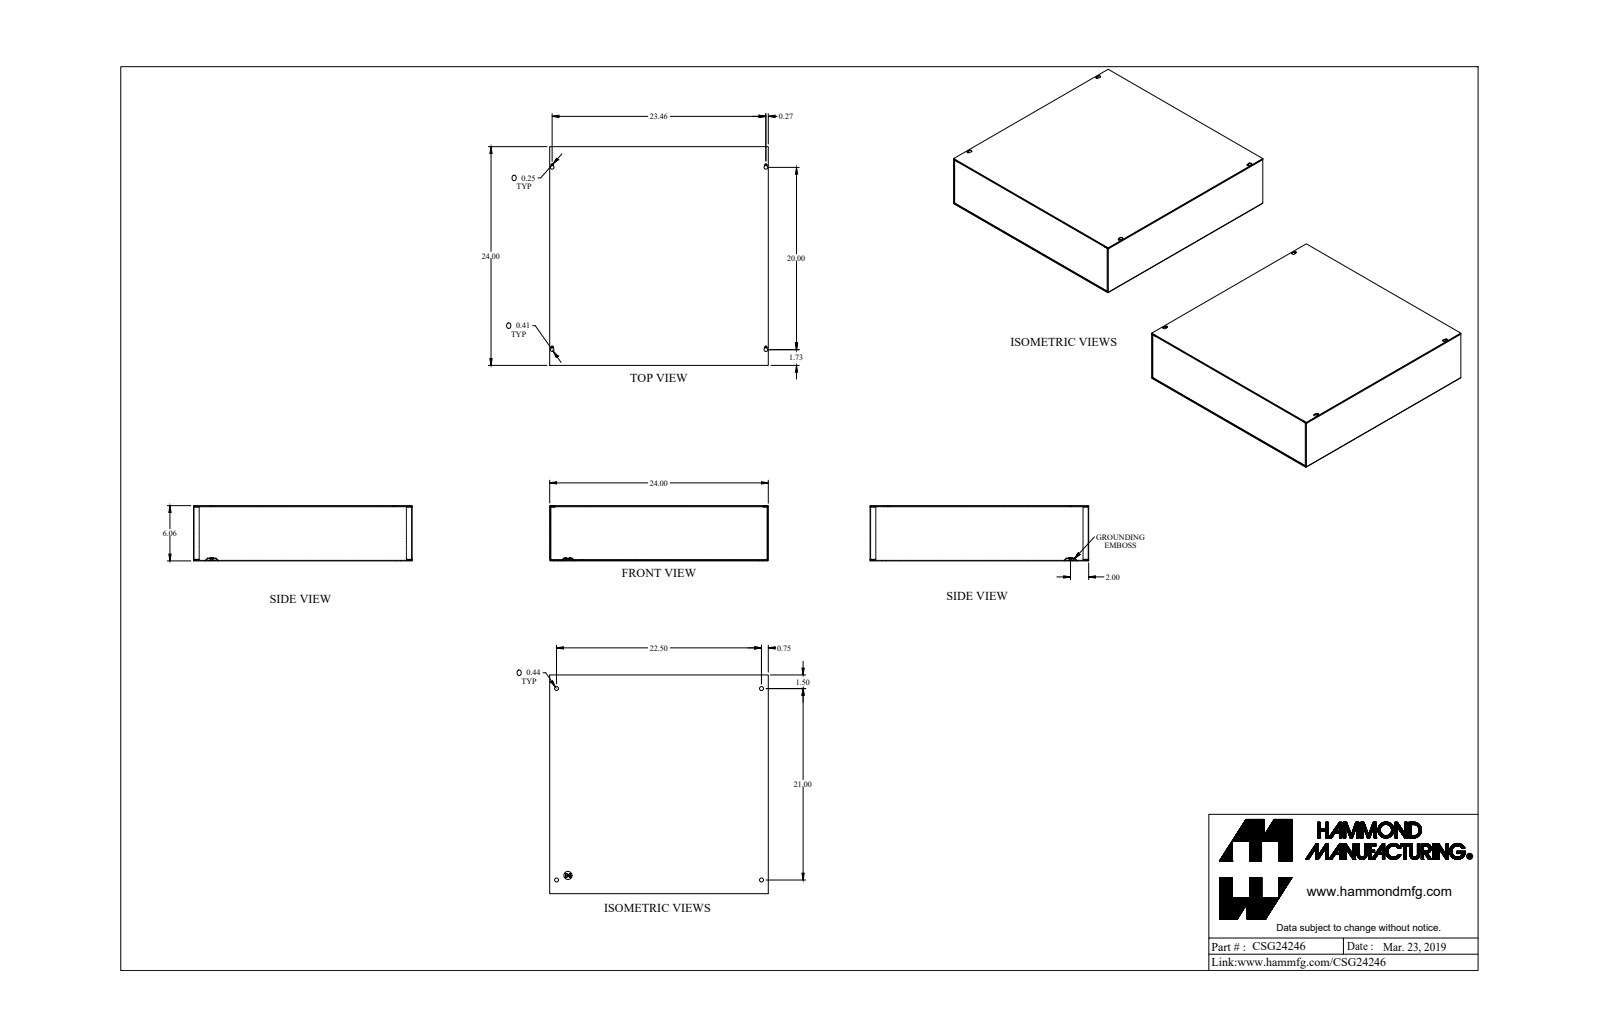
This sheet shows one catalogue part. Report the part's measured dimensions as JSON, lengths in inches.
{"part_name": "CSG24246_Default", "step_written_by": "SolidWorks 2019 (CONFIG_CONTROL_DESIGN)", "units": "inches", "bodies": {"solids": 4, "faces": 205, "planar": 125, "cylindrical": 72, "other": 8}, "overall_size": [24, 24, 6.057], "volume_in3": 102.3, "surface_area_in2": 3610, "round_holes": [[0.17, 5], [0.437, 4], [0.5, 1]], "round_bosses_or_shafts": [[0.492, 1], [0.284, 1]], "partial_cylinders_radius": [[0.029, 12], [0.086, 12], [0.057, 8], [0.125, 4], [0.203, 4]], "face_to_face_distances": [0.057, 6, 5.943, 6.057, 23.943, 24, 23.886, 0.08, 5.863, 5.92], "hole_center_spacings": [0.693, 20.506, 22.985, 30.795, 20, 21, 22.5, 23.46]}
